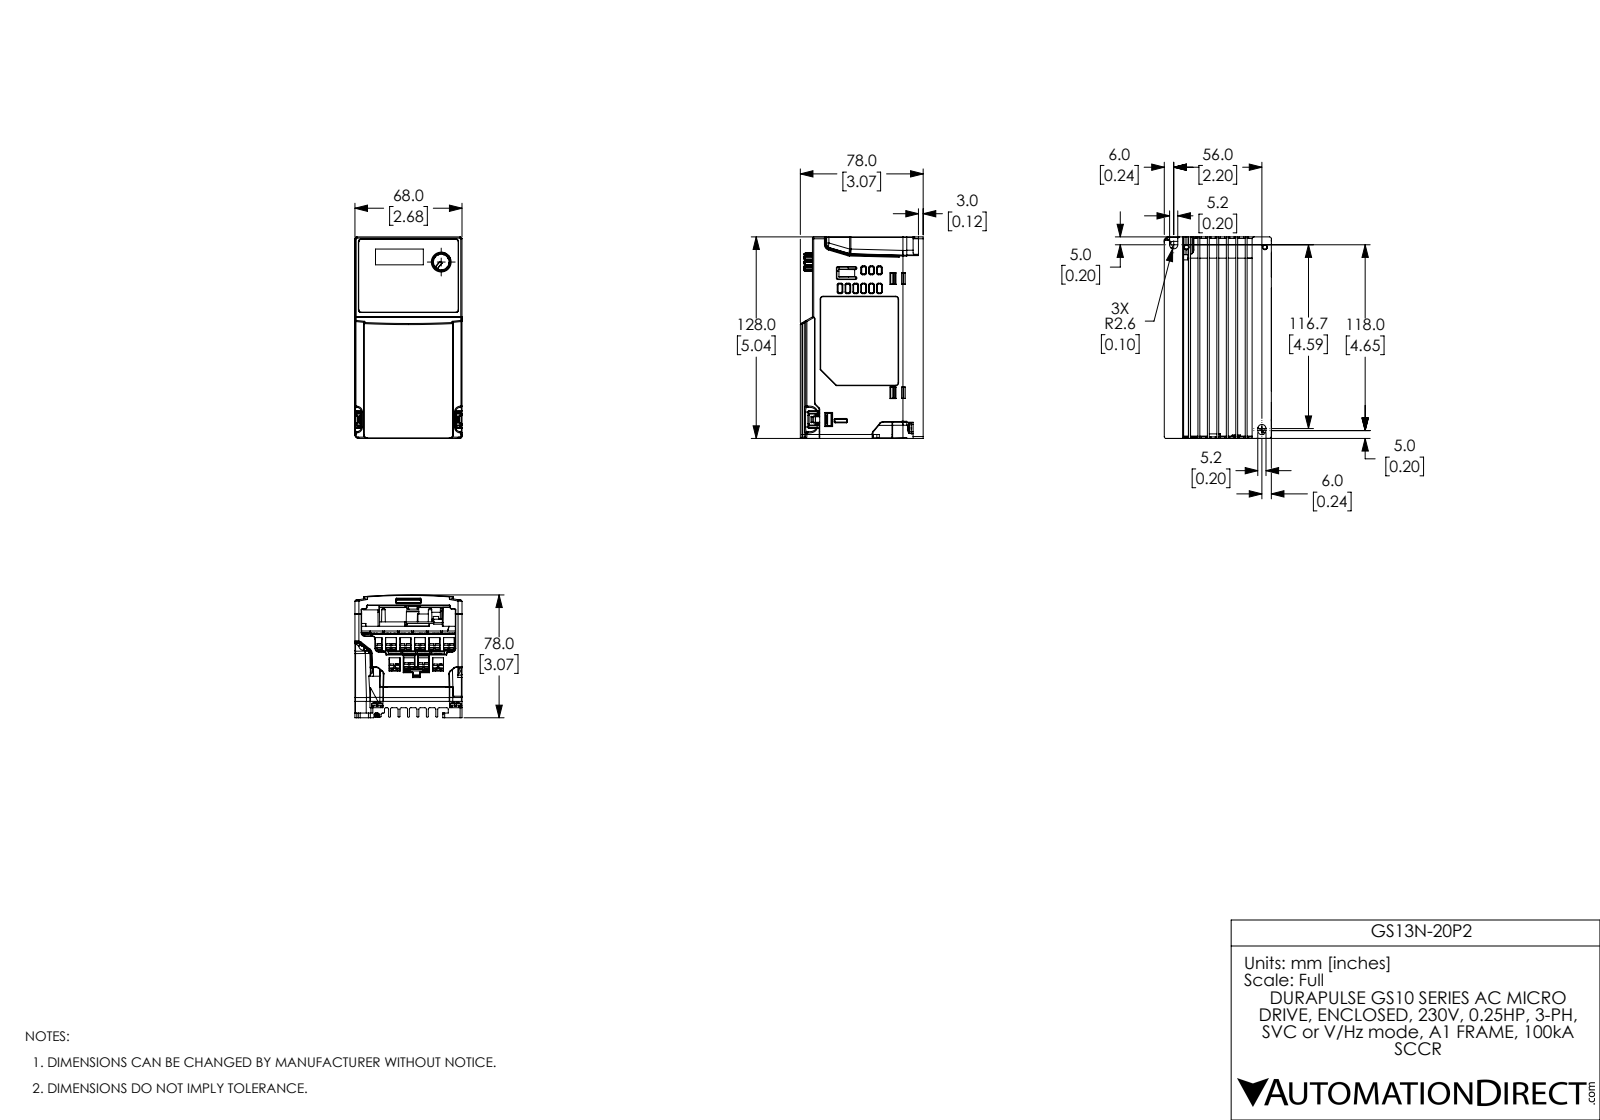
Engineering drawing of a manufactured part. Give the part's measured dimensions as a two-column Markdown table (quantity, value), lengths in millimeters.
| quantity | value |
| --- | --- |
| part name | DELTA_IA_MDS_VFD-ME300-A1_D-3D_20190924 Red1 ext1 r1 wo bottom 1B COMPLETE 1 cmb1 B |
| STEP written by | SolidWorks 2017 (AUTOMOTIVE_DESIGN) |
| units | millimeters |
| bodies | 25 solids, 5297 faces (2899 planar, 1150 cylindrical, 1248 other) |
| overall size | 128 × 78 × 68 |
| volume | 416 900 mm³ |
| surface area | 127 700 mm² |
| round holes (diameter × count) | 2.8 × 10, 3.3 × 2, 4.8 × 2, 3.9 × 1, 10.9 × 1, 12.6 × 1 |
| round bosses / shafts (diameter × count) | 6.8 × 12, 2.8 × 12, 3.5 × 10, 4.2 × 2, 3.4 × 1 |
| partial cylindrical surfaces (radius × count) | 0.3 × 145, 0.5 × 144, 0.2 × 65, 0.4 × 53, 1 × 39, 0.8 × 28, 2 × 26, 3 × 24 |
| main face-to-face distances | 1.1, 66.9, 68, 65.8, 1, 55.3, 67.9, 2.4, 57.7, 96.8 |
| hole center spacings | 9.2, 18.4, 14.4, 15.7, 18.2, 27.6, 20.9, 21.4 |
